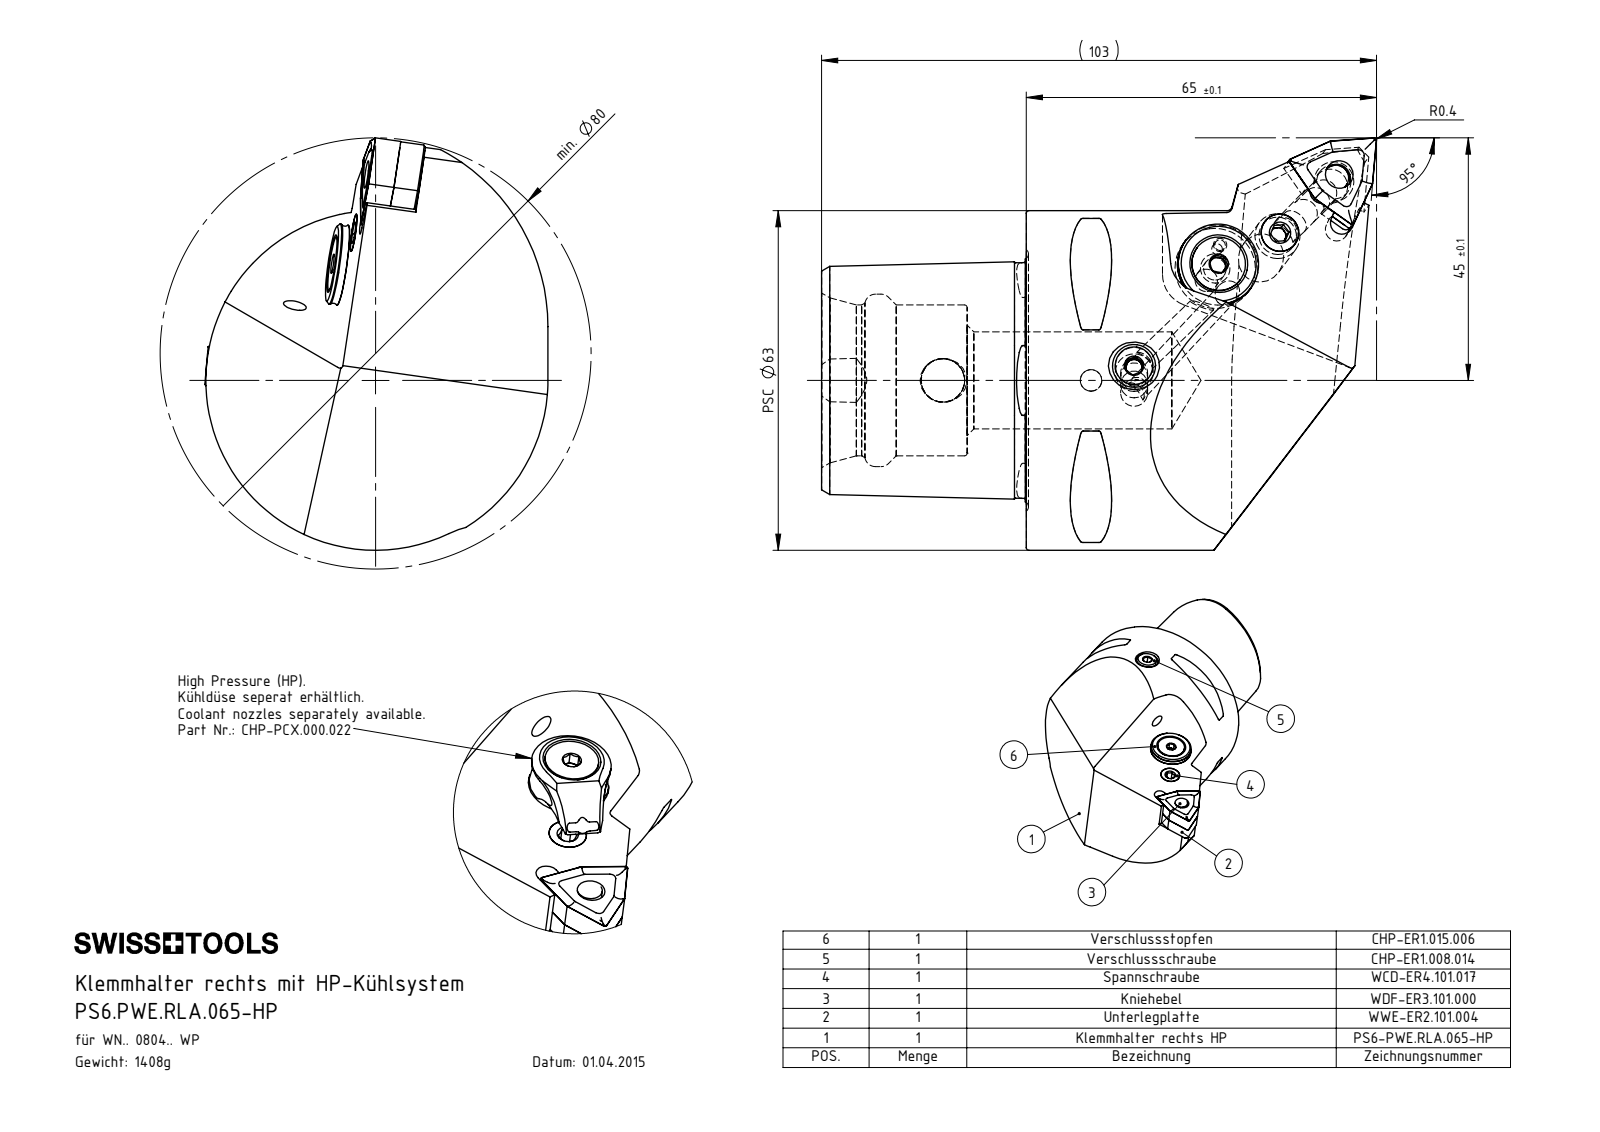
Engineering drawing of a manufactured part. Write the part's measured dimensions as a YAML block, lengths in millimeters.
part_name: "DIN 3771 - 13x1; ISO 8752 2x8; PS6.PWE.RLA.065-HP; CHP-ER1.015.006 (+8 more)"
step_written_by: "SolidWorks 2017 (AUTOMOTIVE_DESIGN)"
units: millimeters
bodies: {solids: 11, faces: 466, planar: 141, cylindrical: 116, other: 209}
overall_size: [103, 77, 64]
volume: 188465
surface_area: 34971
round_holes:
  - {diameter: 4.2, count: 2}
  - {diameter: 5, count: 2}
  - {diameter: 7, count: 2}
  - {diameter: 1.2, count: 1}
  - {diameter: 2, count: 1}
  - {diameter: 2.5, count: 1}
  - {diameter: 3, count: 1}
  - {diameter: 4, count: 1}
  - {diameter: 5.16, count: 1}
  - {diameter: 5.2, count: 1}
  - {diameter: 6.7, count: 1}
  - {diameter: 7.8, count: 1}
round_bosses_or_shafts:
  - {diameter: 8, count: 2}
  - {diameter: 63, count: 1}
  - {diameter: 15, count: 1}
  - {diameter: 13.4, count: 1}
  - {diameter: 10, count: 1}
  - {diameter: 7.9, count: 1}
  - {diameter: 6.4, count: 1}
  - {diameter: 5.5, count: 1}
partial_cylinders:
  - {radius: 0.5, count: 10}
  - {radius: 0.4, count: 3}
  - {radius: 1, count: 3}
  - {radius: 2.5, count: 3}
  - {radius: 2.1, count: 1}
  - {radius: 2.3, count: 1}
  - {radius: 2.35, count: 1}
  - {radius: 2.8, count: 1}
face_to_face_distances: [38, 24.88, 4.76, 4.46, 27, 11, 9.22, 55.8, 4.85, 4.5]
hole_center_spacings: [24.05, 4.48, 15.6, 27.25, 27.26, 4.47, 4.5, 9.9]
